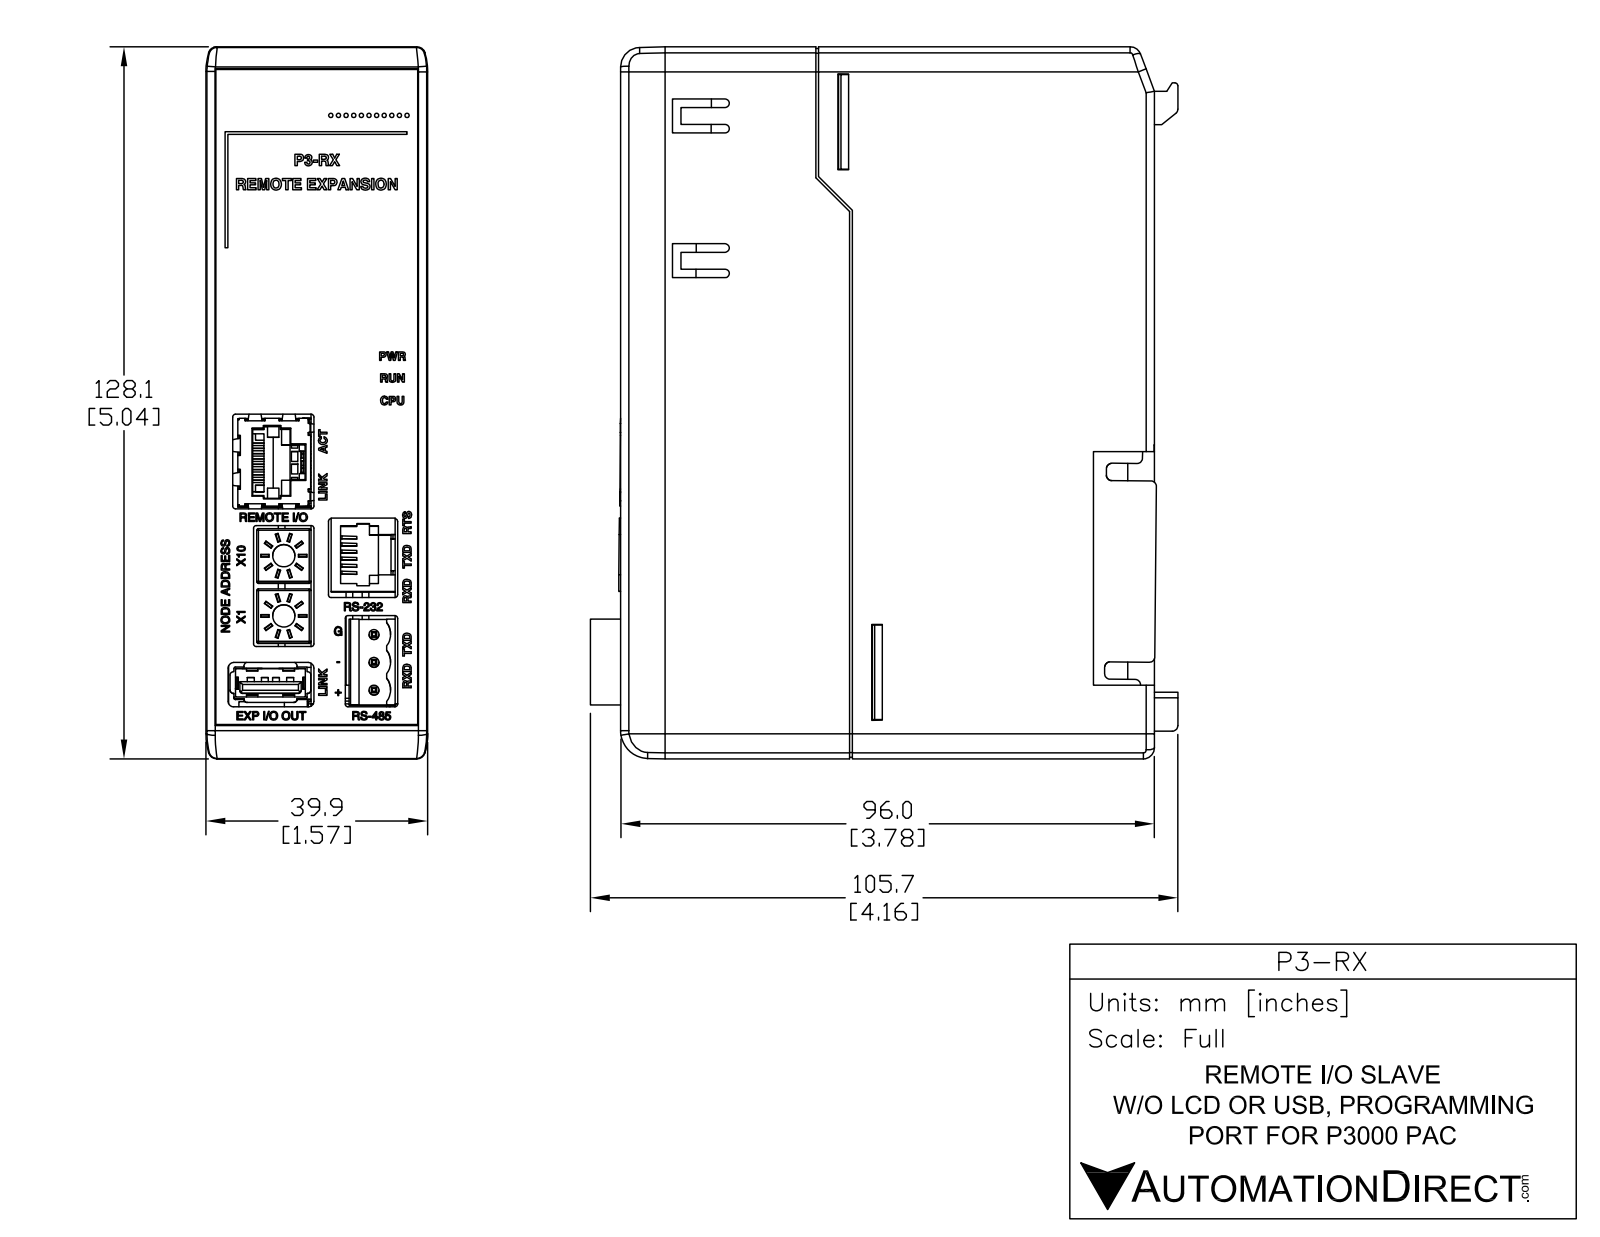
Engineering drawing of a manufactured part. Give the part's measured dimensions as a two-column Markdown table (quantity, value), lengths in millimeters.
| quantity | value |
| --- | --- |
| part name | P3-RX |
| STEP written by | SolidWorks 2012 (AUTOMOTIVE_DESIGN) |
| units | millimeters |
| bodies | 2 solids, 651 faces (524 planar, 52 cylindrical, 75 other) |
| overall size | 131.75 × 126.7 × 39.5 |
| volume | 482 677 mm³ |
| surface area | 51 809 mm² |
| round holes (diameter × count) | 3.55 × 3, 4 × 2 |
| partial cylindrical surfaces (radius × count) | 1 × 22, 0.5 × 13, 0.45 × 1 |
| main face-to-face distances | 39.5, 96, 0.5, 128, 127.5, 1, 95, 10, 127, 55.05 |
| hole center spacings | 5.2, 10.37, 10.4, 17.29, 18.63, 21.18, 21.2, 24.59 |
